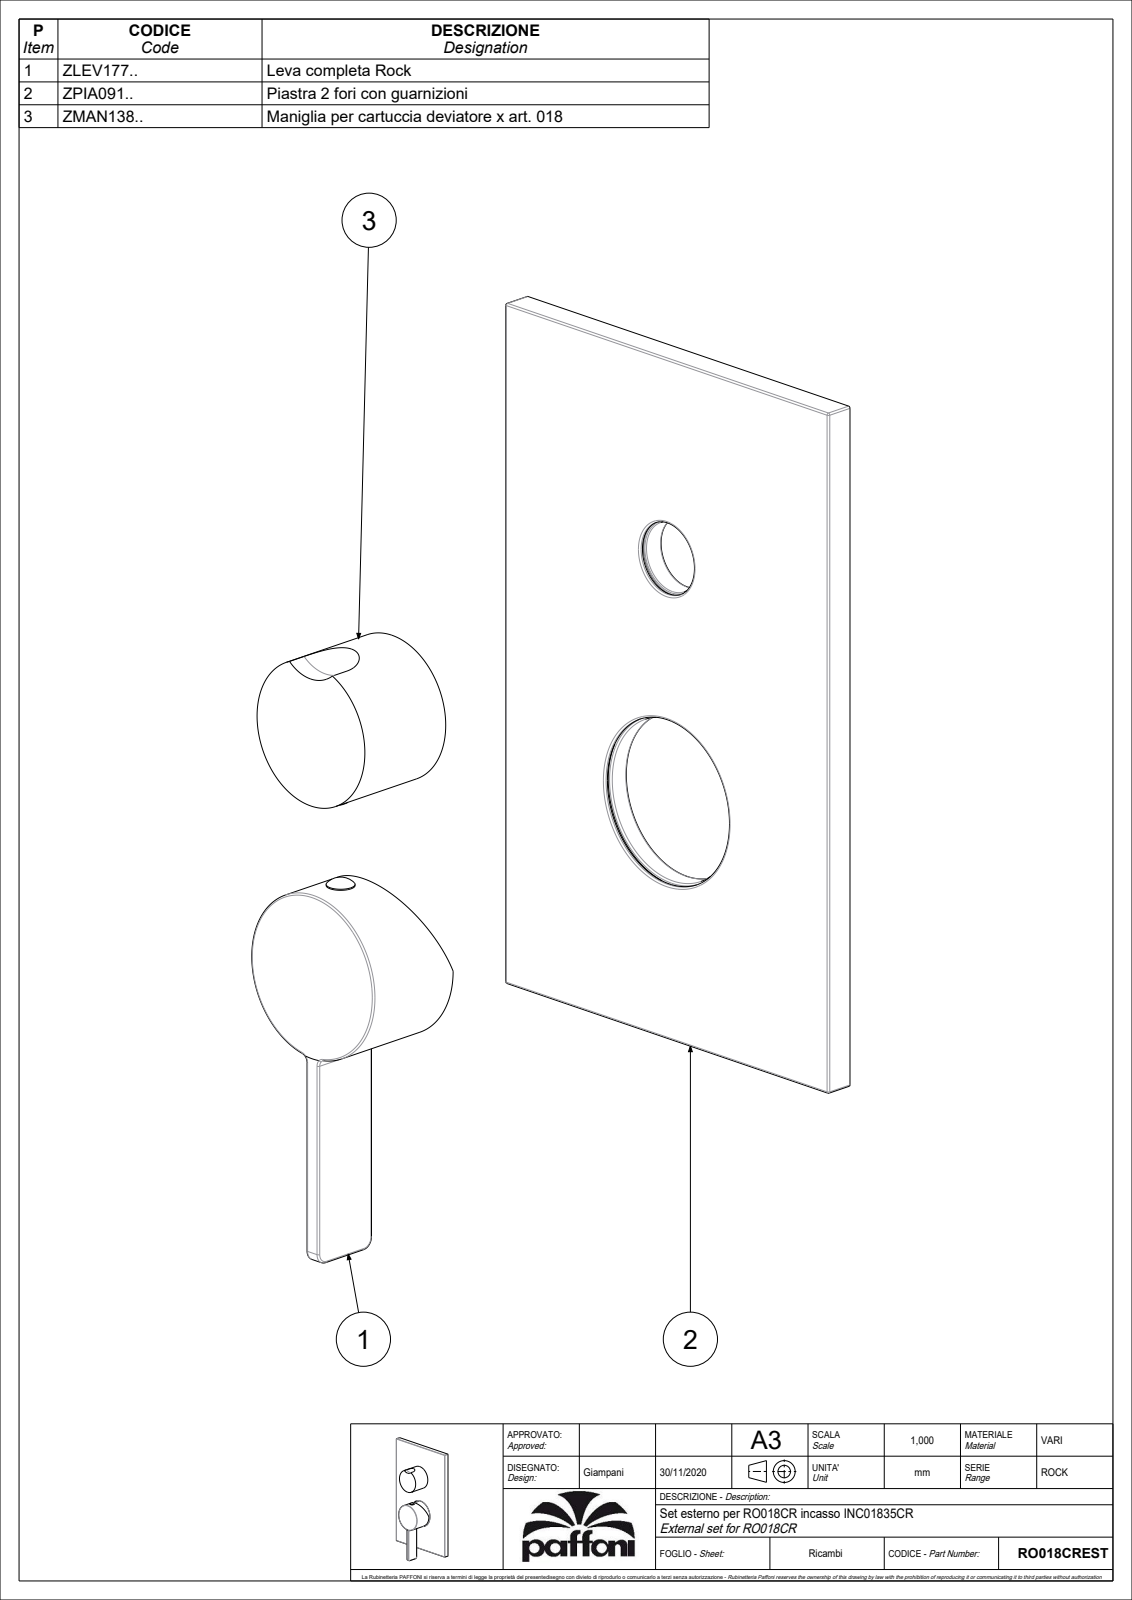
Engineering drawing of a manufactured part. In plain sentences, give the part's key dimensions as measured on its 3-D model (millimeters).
The part is named "RO018CREST". Its 3-D file was written by "CREO PARAMETRIC BY PTC INC, 2020044 (CONFIG_CONTROL_DESIGN)". It is 3 solids with 288 faces: 99 planar, 100 cylindrical and 89 other. Overall it measures 204 by 120 by 40.35 millimeters. Its volume is 157 034 cubic millimeters and its surface area 99 891 square millimeters. Round holes: 2 of diameter 3, 1 of diameter 3.2, 1 of diameter 4.2, 1 of diameter 14.8, 1 of diameter 19.2, 1 of diameter 20, 1 of diameter 21, 1 of diameter 23.2, 1 of diameter 36, 1 of diameter 45, 1 of diameter 46, 1 of diameter 47. Round bosses or shafts: 2 of diameter 7.6, 2 of diameter 5.5, 1 of diameter 51, 1 of diameter 49, 1 of diameter 45.5, 1 of diameter 40, 1 of diameter 25, 1 of diameter 24. Partial cylindrical surfaces (rounded edges, fillets, slot ends): 17 of radius 0.5, 8 of radius 1, 2 of radius 0.3, 2 of radius 1.5, 2 of radius 2, 2 of radius 3, 1 of radius 3.5, 1 of radius 12.5. The main face-to-face distances are 2.5, 8, 5.5, 0.5, 5, 3, 22.5, 57.75, 62.25, 4.5. The hole center spacings are 1, 10, 68, 78.
